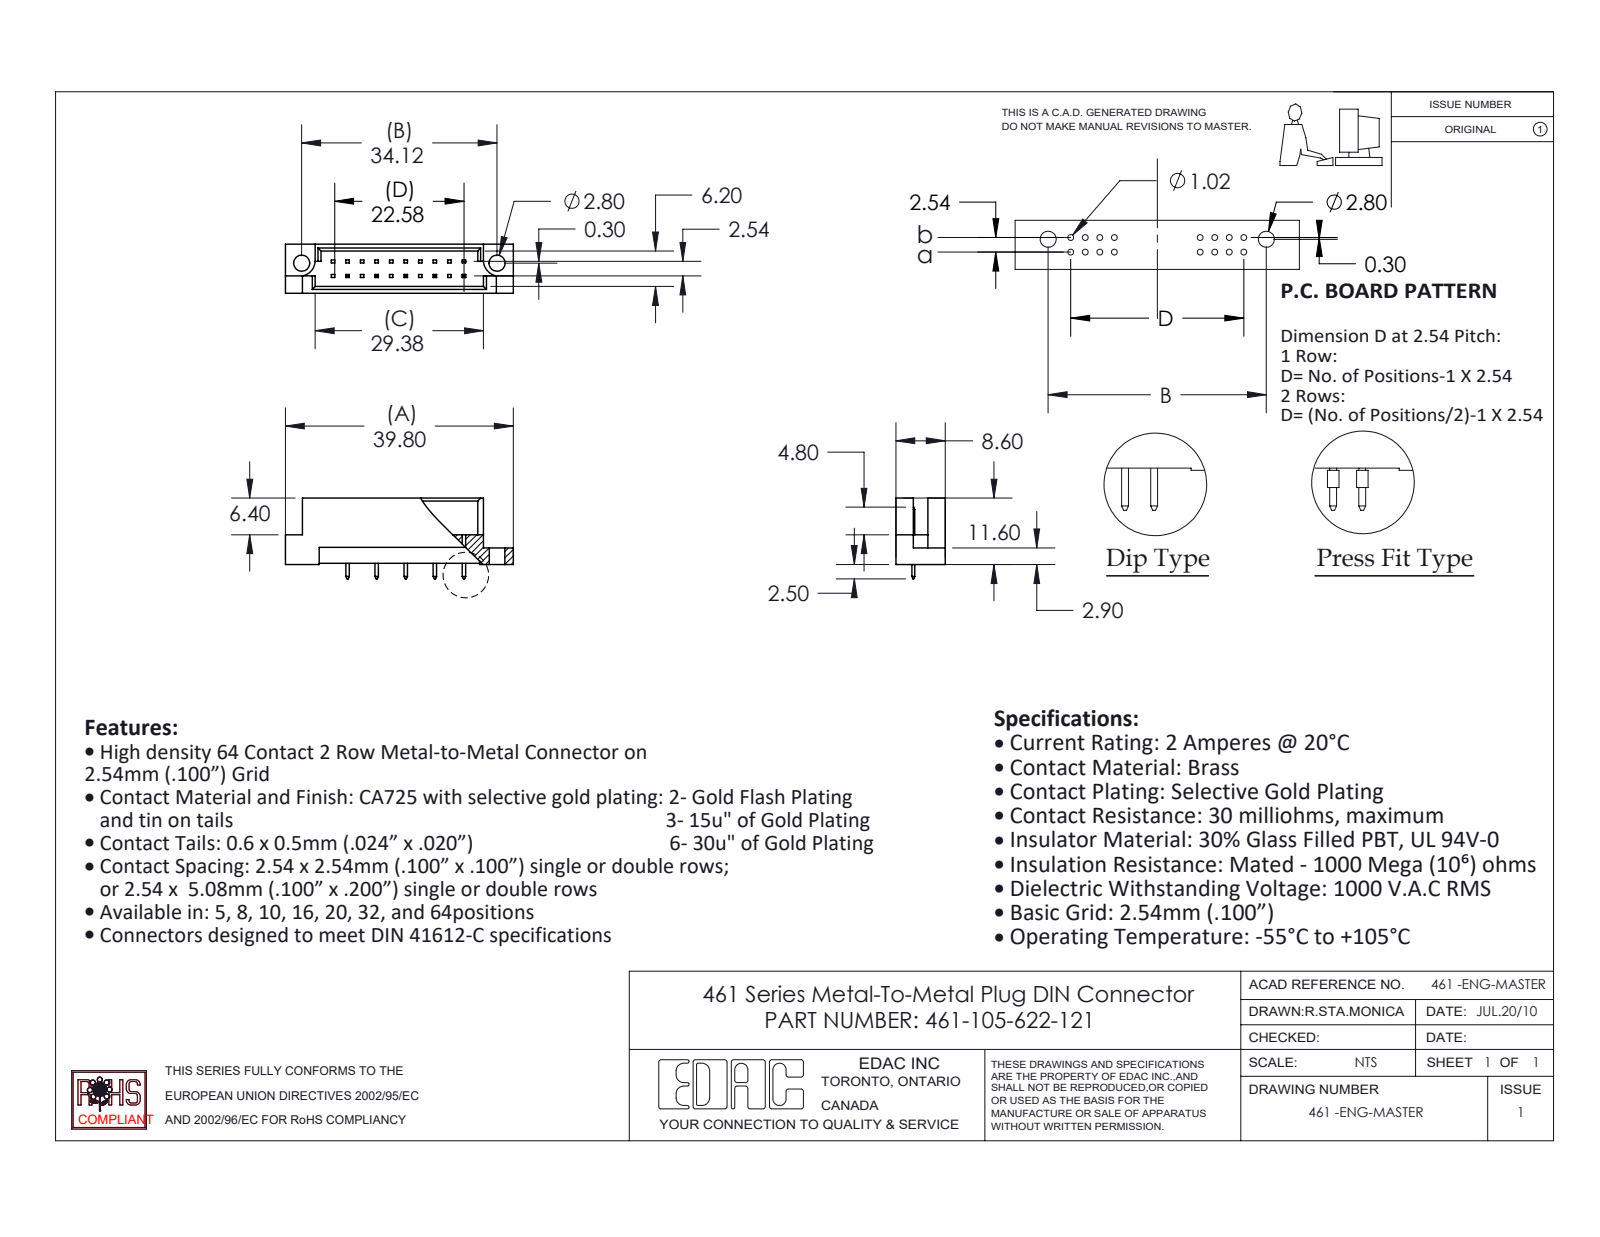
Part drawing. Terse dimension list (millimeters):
name: 461 Part_20; 461-105-622-121; 461-290_22
written by: SolidWorks 2020 (CONFIG_CONTROL_DESIGN)
unit: mm
bodies: 6 solids, 198 faces (192 planar, 6 cylindrical, 0 other)
size: 39.8 × 14.1 × 8.6
volume: 1 923 mm³; area: 2 473 mm²
holes: 2× ⌀2.8
rounds: 2× R2.8
face distances: 1.2, 7.4, 8.6, 6.2, 5, 3.28, 5.32, 2.08, 4.12, 2.78
hole spacings: 34.12
